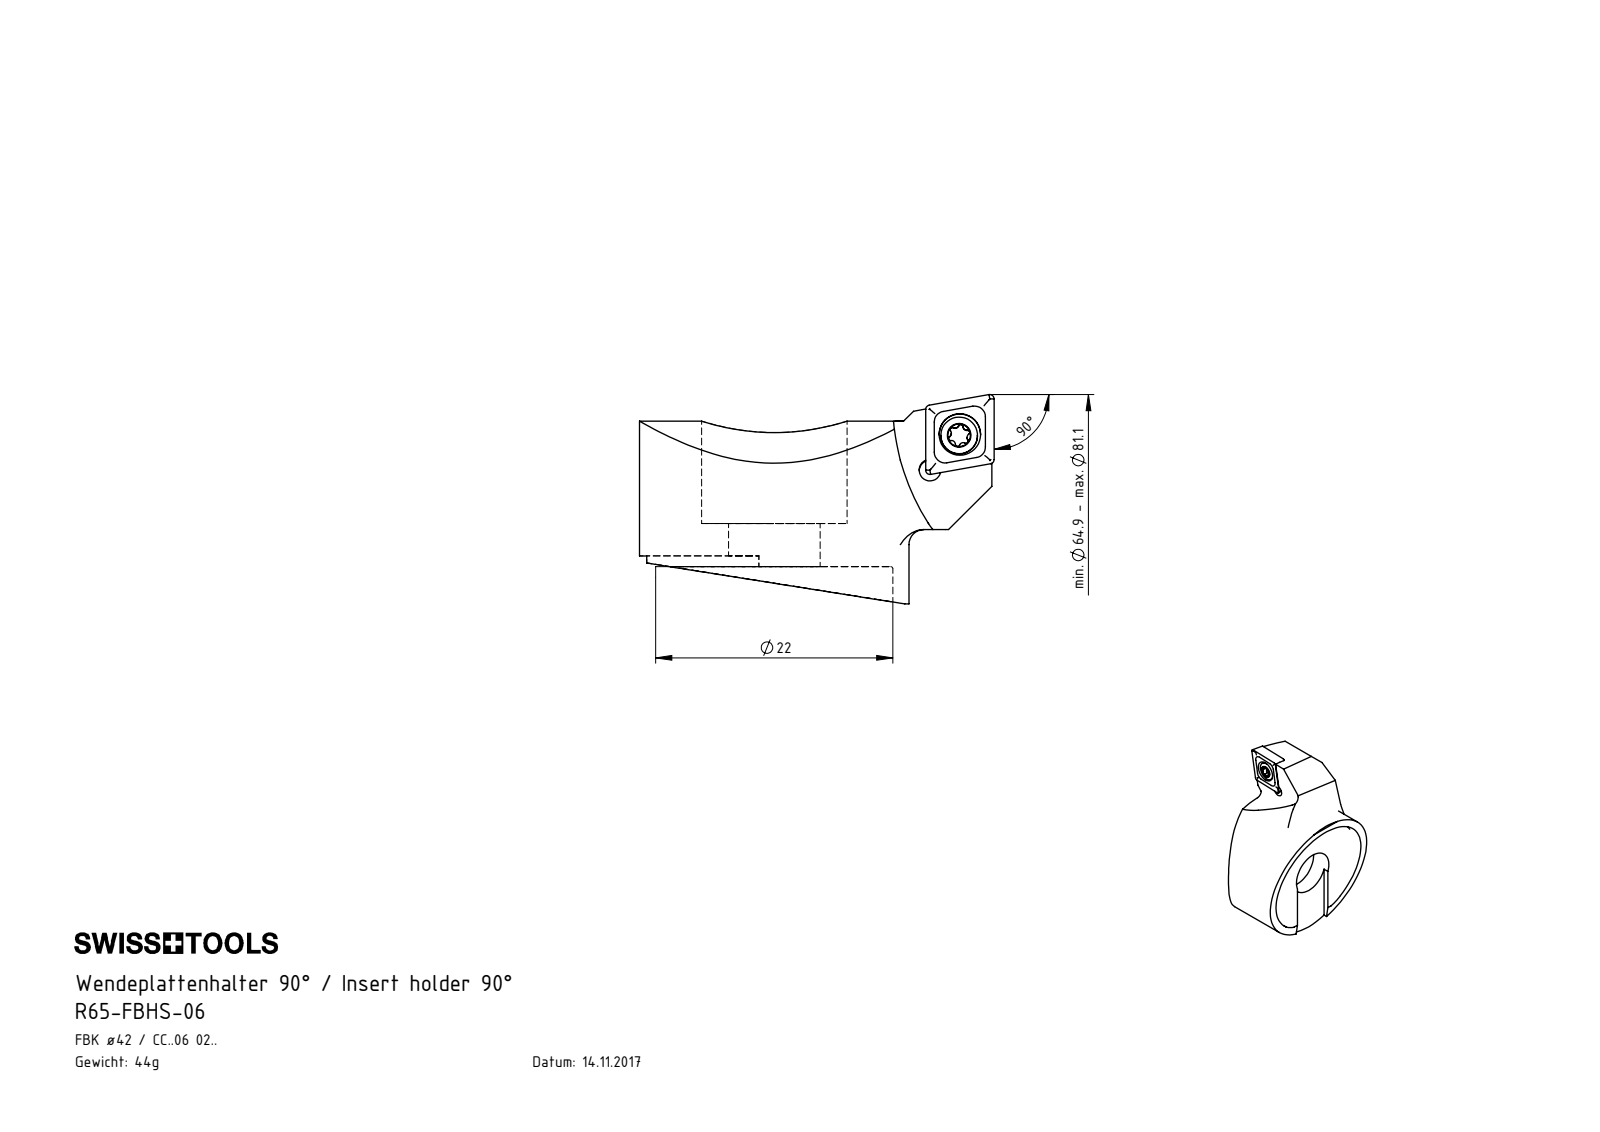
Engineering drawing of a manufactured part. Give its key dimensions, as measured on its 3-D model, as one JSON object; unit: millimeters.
{"part_name": "F42-WCA.001.016_A_fertigbearbeitet; CCMT060204; WCA-ER2.001.006_A; R65-FBHS-06", "step_written_by": "SolidWorks 2017 (CONFIG_CONTROL_DESIGN)", "units": "millimeters", "bodies": {"solids": 5, "faces": 151, "planar": 48, "cylindrical": 47, "other": 56}, "overall_size": [32.9, 25, 19.5], "volume_mm3": 5625, "surface_area_mm2": 3551, "round_holes": [[2.05, 1], [2.1, 1], [2.8, 1], [3.85, 1], [8.5, 1], [13.5, 1]], "round_bosses_or_shafts": [[24.25, 1], [3.4, 1], [2.5, 1]], "partial_cylinders_radius": [[0.21, 6], [0.36, 5], [0.5, 2], [0.36, 1], [5, 1], [11, 1], [12.5, 1], [16, 1]], "face_to_face_distances": [14, 13.7, 11.5, 11.2, 2.5, 2.28, 13, 12.7, 1.5, 1], "hole_center_spacings": [3.84, 4]}
